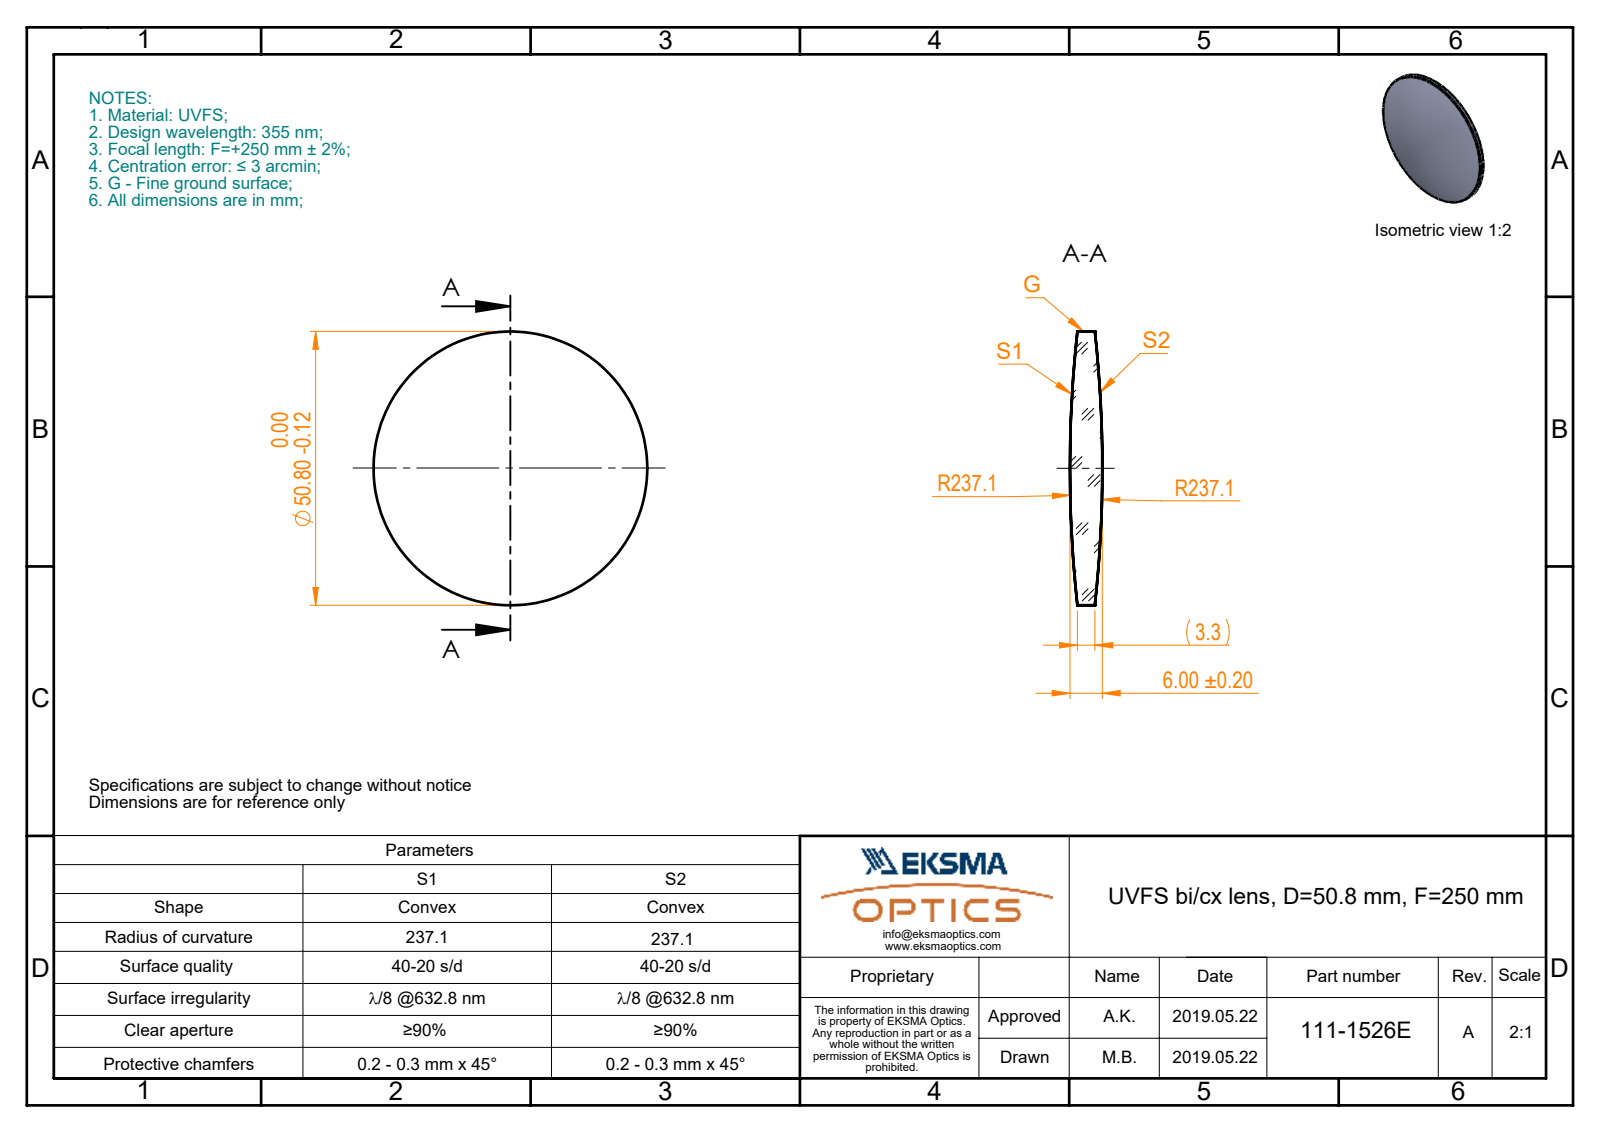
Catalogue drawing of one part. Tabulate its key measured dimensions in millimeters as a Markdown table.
| quantity | value |
| --- | --- |
| part name | 111-1526E UVFS bi-cx 50.8 F250 |
| STEP written by | SolidWorks 2017 (CONFIG_CONTROL_DESIGN) |
| units | millimeters |
| bodies | 1 solid, 6 faces (0 planar, 2 cylindrical, 4 other) |
| overall size | 50.8 × 50.8 × 6 |
| volume | 9 398 mm³ |
| surface area | 4 587 mm² |
| round bosses / shafts (diameter × count) | 50.8 × 1 |
